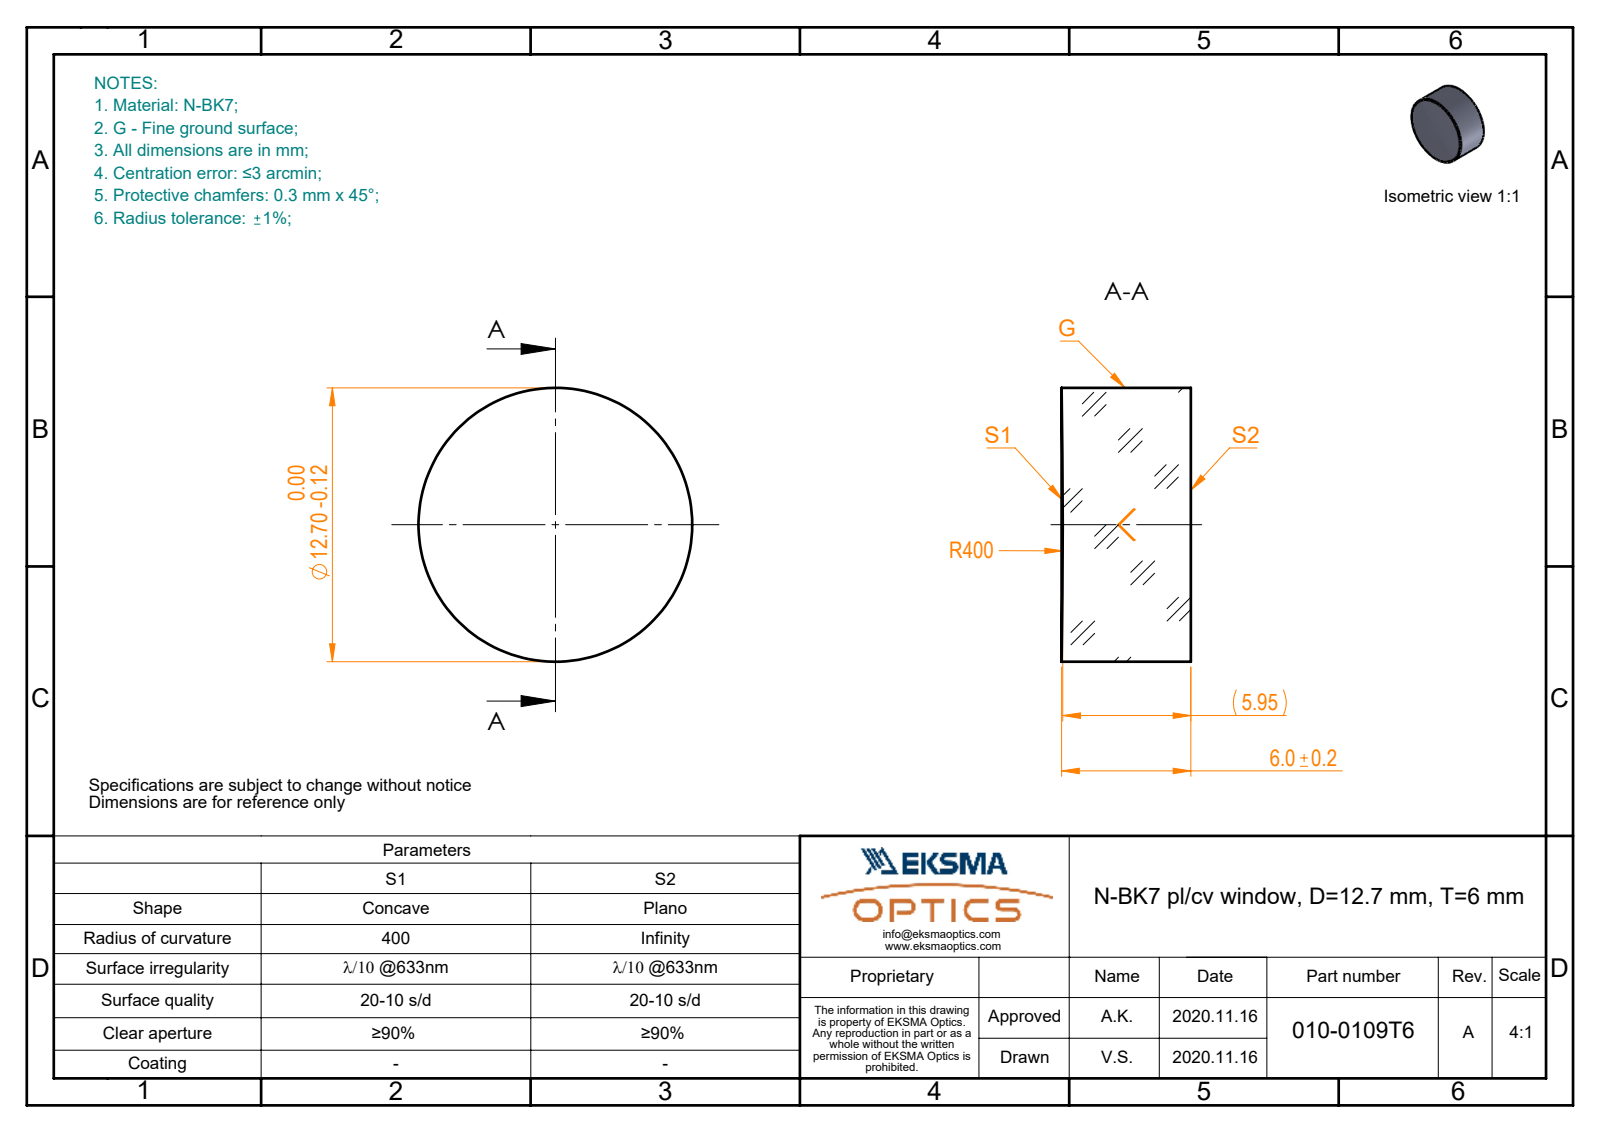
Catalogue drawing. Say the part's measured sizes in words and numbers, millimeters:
The part is named "010-0109T6_N-BK7_PCV_window". Its 3-D file was written by "SolidWorks 2019 (CONFIG_CONTROL_DESIGN)". It is 1 solid with 5 faces: 1 planar, 2 cylindrical and 2 other. Overall it measures 12.7 by 12.7 by 6 millimeters. Its volume is 757 cubic millimeters and its surface area 493 square millimeters. Round bosses or shafts: 1 of diameter 12.7.
